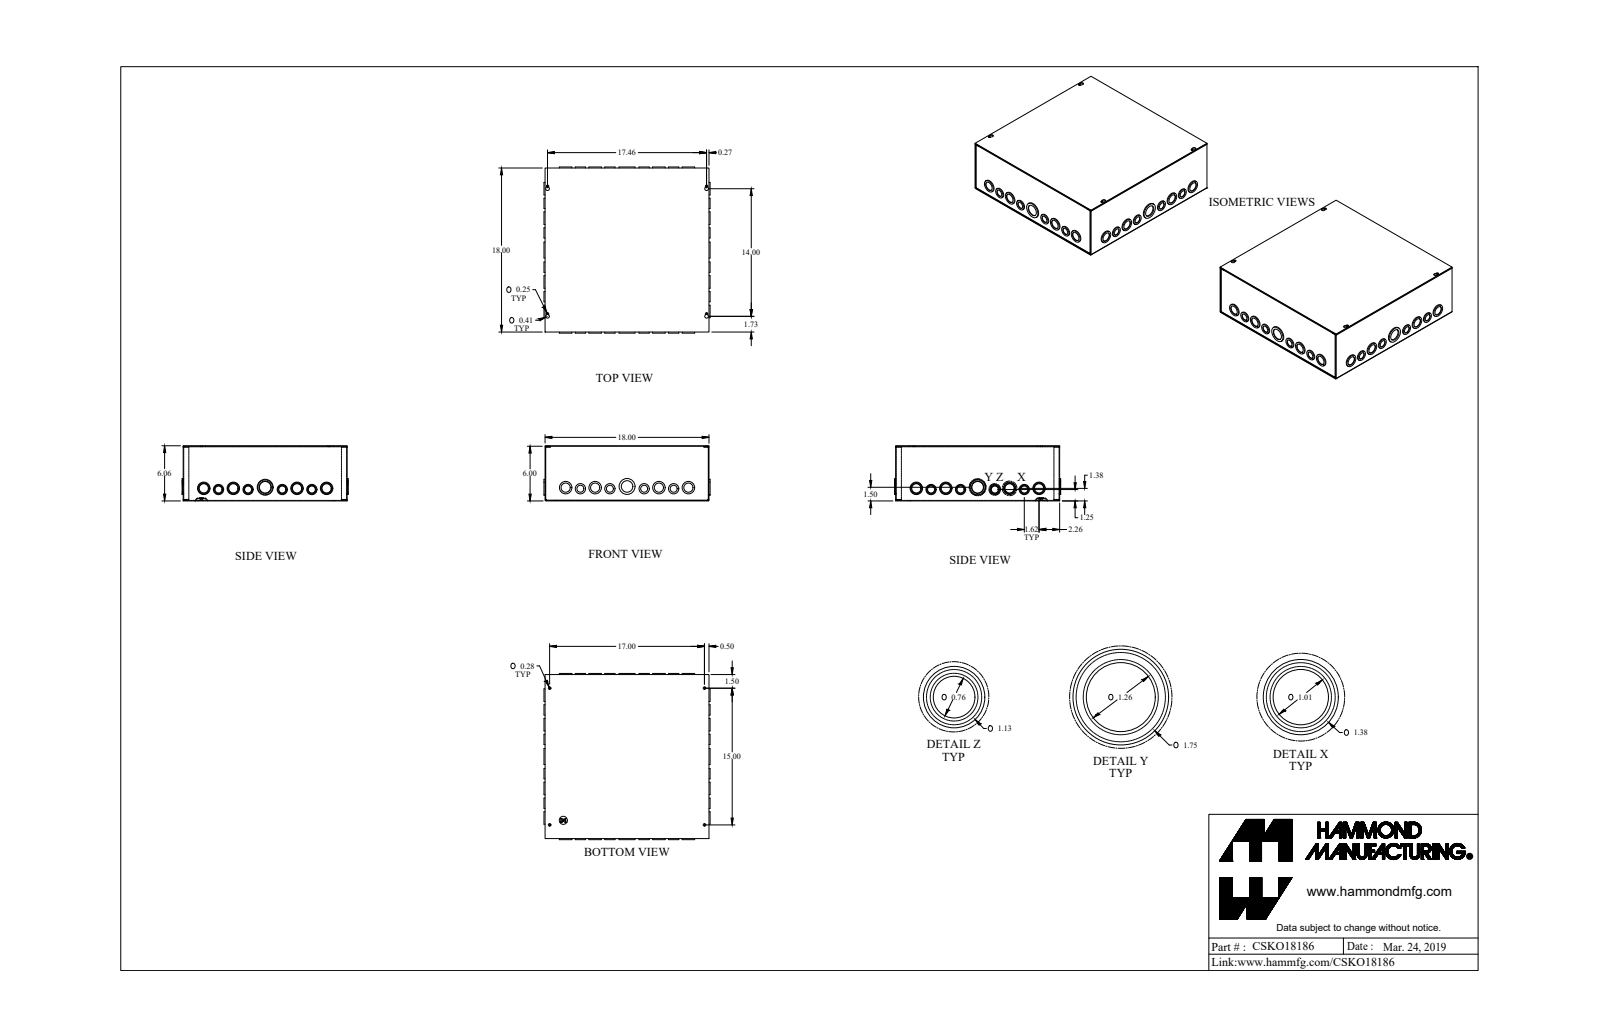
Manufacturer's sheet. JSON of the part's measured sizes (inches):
{"part_name": "CSKO18186_Default", "step_written_by": "SolidWorks 2019 (CONFIG_CONTROL_DESIGN)", "units": "inches", "bodies": {"solids": 4, "faces": 637, "planar": 269, "cylindrical": 360, "other": 8}, "overall_size": [18.234, 18.234, 6.057], "volume_in3": 65.9, "surface_area_in2": 2329, "round_holes": [[1.011, 16], [1.261, 10], [0.761, 8], [0.17, 5], [0.281, 4], [1.636, 2], [0.5, 1]], "round_bosses_or_shafts": [[1.125, 14], [1.375, 9], [0.875, 8], [0.875, 6], [1.125, 4], [1.375, 3], [1.75, 2], [0.492, 1]], "partial_cylinders_radius": [[0.029, 12], [0.086, 12], [0.057, 8], [0.125, 4], [0.203, 4]], "face_to_face_distances": [0.057, 6, 17.943, 5.943, 6.057, 18, 17.886, 0.114, 0.08, 5.863], "hole_center_spacings": [1.625, 3.24, 8.621, 7, 10.24, 0.55, 1.896, 3.502]}
